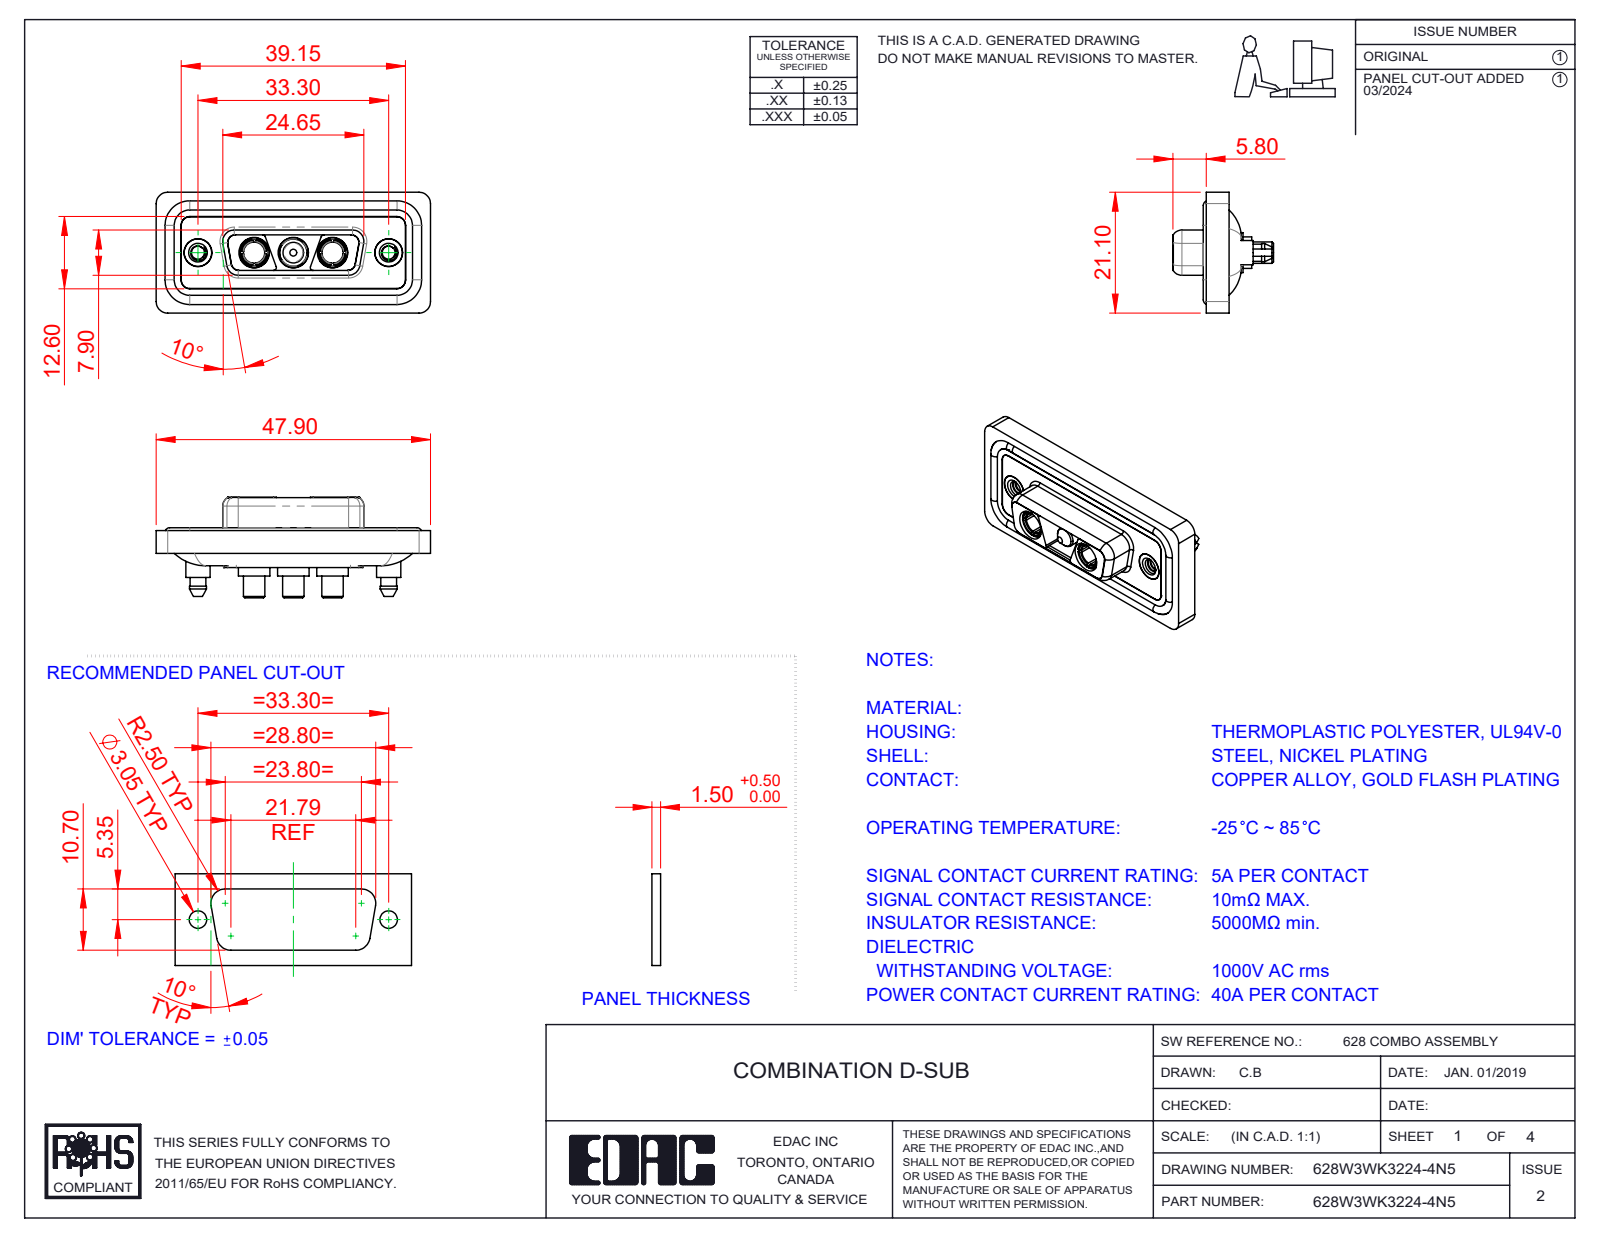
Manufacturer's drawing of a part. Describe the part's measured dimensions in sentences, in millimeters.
The part is named "628Combo Waterproof Housing_15 Contacts; Power Socket_40A S; 628Combo Shell Rear_15 Contacts; 628Combo Threaded Boardlock_5 (+4 more)". Its 3-D file was written by "SolidWorks 2023 (CONFIG_CONTROL_DESIGN)". It is 13 solids with 633 faces: 194 planar, 290 cylindrical and 149 other. Overall it measures 47.9 by 21.1 by 17.55 millimeters. Its volume is 6 067 cubic millimeters and its surface area 9 870 square millimeters. Round holes: 5 of diameter 4.85, 3 of diameter 5.3, 2 of diameter 2.26, 2 of diameter 3.7, 2 of diameter 4, 2 of diameter 4.05, 2 of diameter 5. Round bosses or shafts: 4 of diameter 1.6, 3 of diameter 5.5, 3 of diameter 5.2, 3 of diameter 4.75, 3 of diameter 3.75, 2 of diameter 5.4, 2 of diameter 4.96, 2 of diameter 4.95. Partial cylindrical surfaces (rounded edges, fillets, slot ends): 24 of radius 1.5, 20 of radius 2, 12 of radius 1.35, 10 of radius 1.6, 8 of radius 0.5, 4 of radius 0.25, 4 of radius 0.6, 4 of radius 0.65. The main face-to-face distances are 0.4, 1.6, 0.5, 1.8, 1.1, 2.9, 5.65, 7.05, 5.35, 1.5. The hole center spacings are 6.85, 9.8, 16.65, 23.5, 13.7, 33.3.
